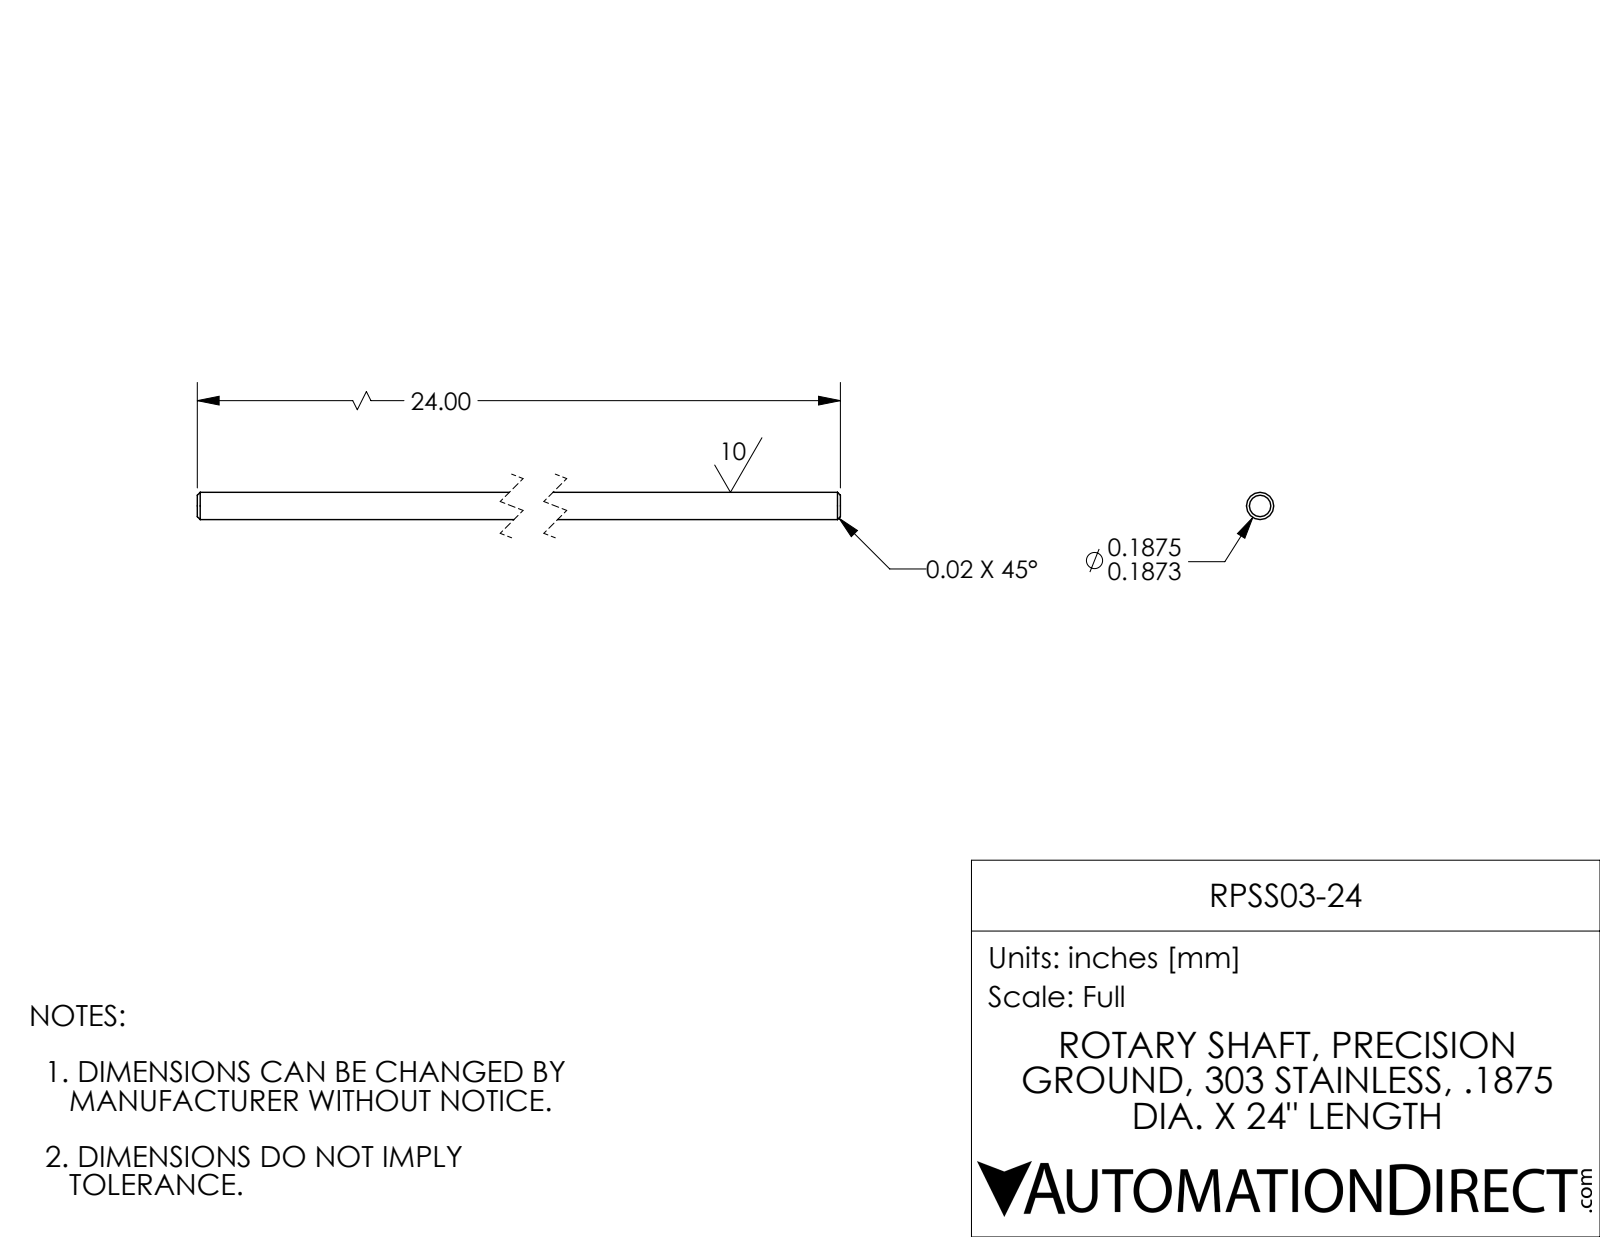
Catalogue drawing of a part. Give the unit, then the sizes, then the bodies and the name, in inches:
Units: inches
Overall size (bounding box): 24 × 0.188 × 0.188
Round bosses / shafts (diameter × count): ⌀0.187 ×1
Main face-to-face distances: 24
Volume: 0.662 in³ · Surface area: 14.18 in²
Bodies: 1 solid, 8 faces (2 planar, 2 cylindrical, 4 other)
Part name (STEP PRODUCT): RPSS03-24
STEP written by: SolidWorks 2017 (AUTOMOTIVE_DESIGN)
